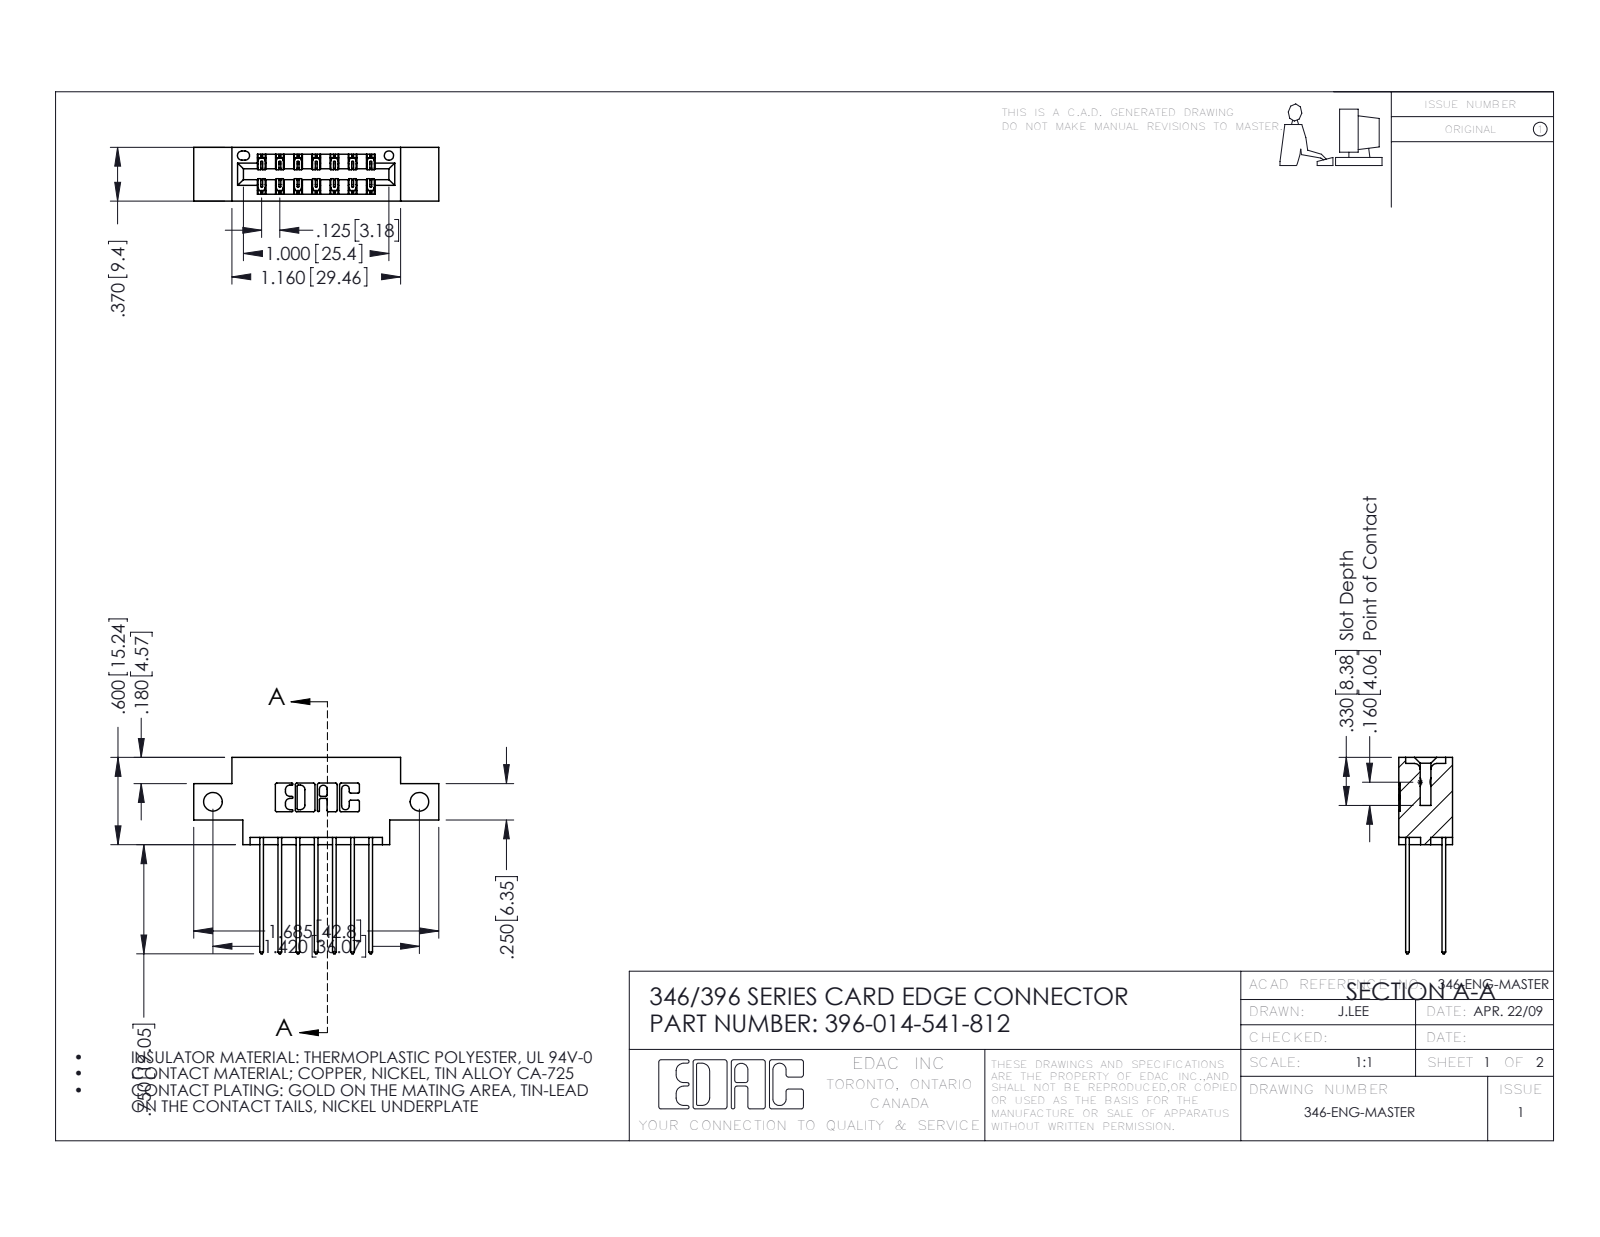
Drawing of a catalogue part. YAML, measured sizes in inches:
part_name: "346 Part_0.170 Offset - Side Mount; 345-292-001_345-293-141; 396-014-541-812"
step_written_by: "SolidWorks 2016 (CONFIG_CONTROL_DESIGN)"
units: inches
bodies: {solids: 15, faces: 854, planar: 570, cylindrical: 284, other: 0}
overall_size: [1.685, 1.35, 0.37]
volume: 0.228
surface_area: 7.778
round_holes:
  - {diameter: 0.128, count: 2}
  - {diameter: 0.064, count: 1}
partial_cylinders:
  - {radius: 0.01, count: 22}
  - {radius: 0.006, count: 21}
  - {radius: 0.01, count: 14}
  - {radius: 0.007, count: 6}
  - {radius: 0.031, count: 6}
  - {radius: 0.026, count: 3}
  - {radius: 0.014, count: 2}
  - {radius: 0.022, count: 2}
face_to_face_distances: [0.25, 0.048, 0.322, 0.37, 0.072, 0.298, 0.025, 0.275, 0.225, 0.148]
hole_center_spacings: [1.42]
